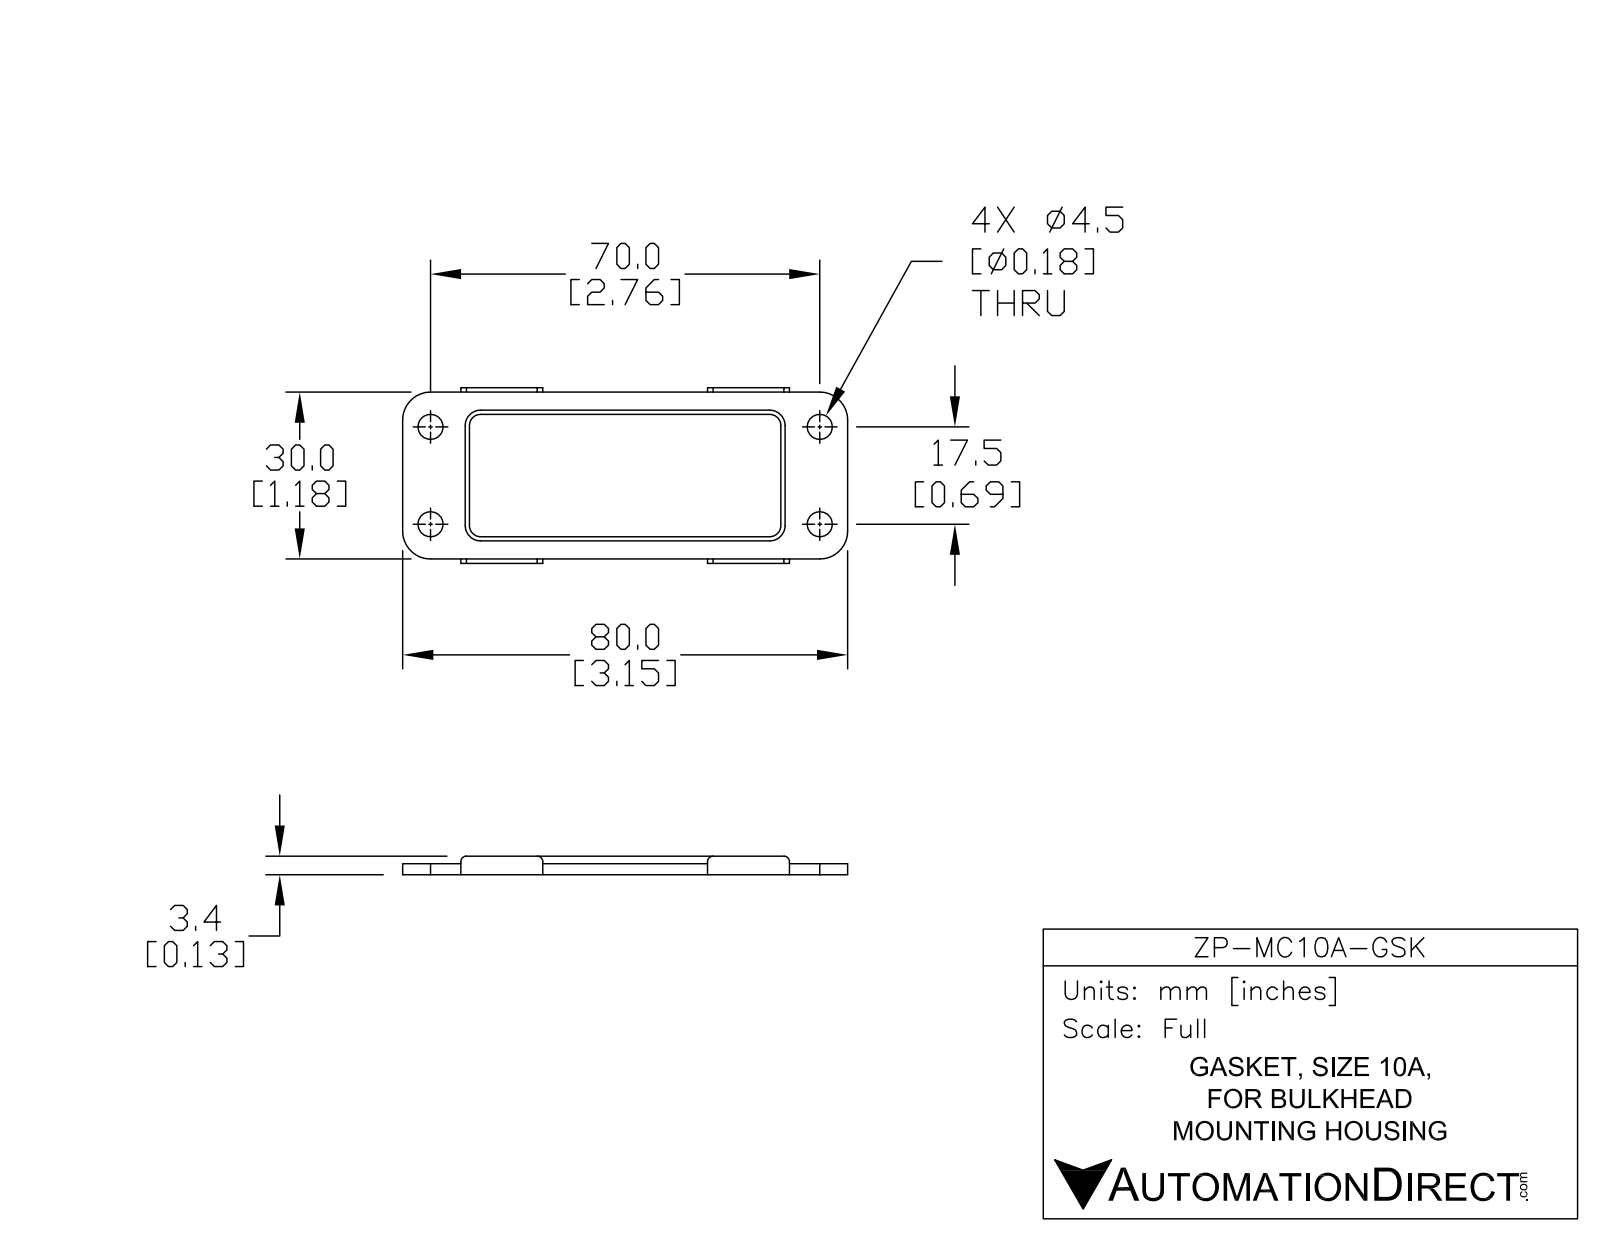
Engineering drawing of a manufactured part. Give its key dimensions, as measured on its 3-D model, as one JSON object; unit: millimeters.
{"part_name": "ZP-MC10A-GSK", "step_written_by": "SolidWorks 2014 (AUTOMOTIVE_DESIGN)", "units": "millimeters", "bodies": {"solids": 1, "faces": 67, "planar": 39, "cylindrical": 28, "other": 0}, "overall_size": [80.4, 31.6, 3.35], "volume_mm3": 2582, "surface_area_mm2": 3769, "round_holes": [[3.5, 4]], "partial_cylinders_radius": [[1, 4], [2, 4], [2.75, 4], [5, 4]], "face_to_face_distances": [2, 4, 26, 0.8, 4.8, 26.8, 30.8, 0.75, 22, 3.35], "hole_center_spacings": [17.5, 70, 72.15]}
